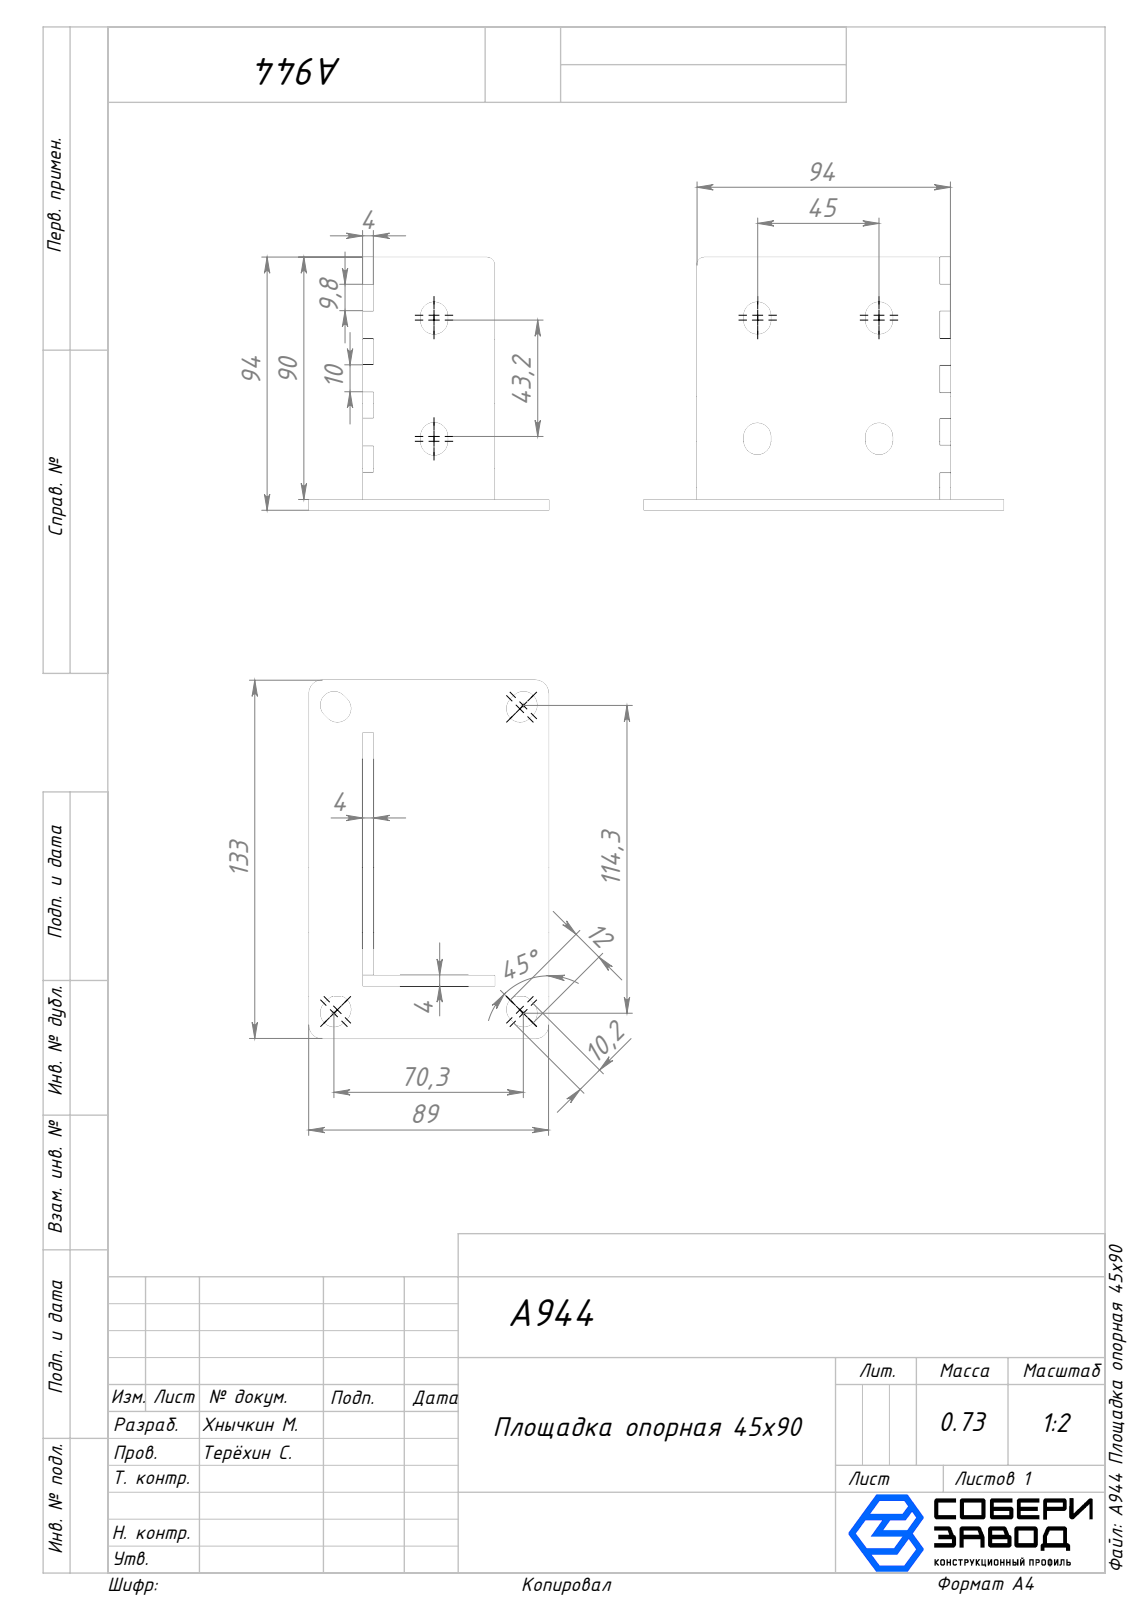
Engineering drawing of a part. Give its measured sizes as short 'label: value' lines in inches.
name: A944 45x90 Боковина с пазом 1_00; A944 45x90 Основание_00; A944 45x90 Боковина с пазом 2_00; A944 Площадка опорная 45x90
written by: SolidWorks 2025 (AUTOMOTIVE_DESIGN)
unit: in
bodies: 3 solids, 120 faces (86 planar, 34 cylindrical, 0 other)
size: 5.236 × 3.701 × 3.504
volume: 5.68 in³; area: 82.79 in²
rounds: 20× R0.201, 4× R0.197, 2× R0.118
face distances: 0.157, 0.787, 3.701, 3.543, 2.717, 0.165, 0.768, 4.469, 0.945, 3.504
